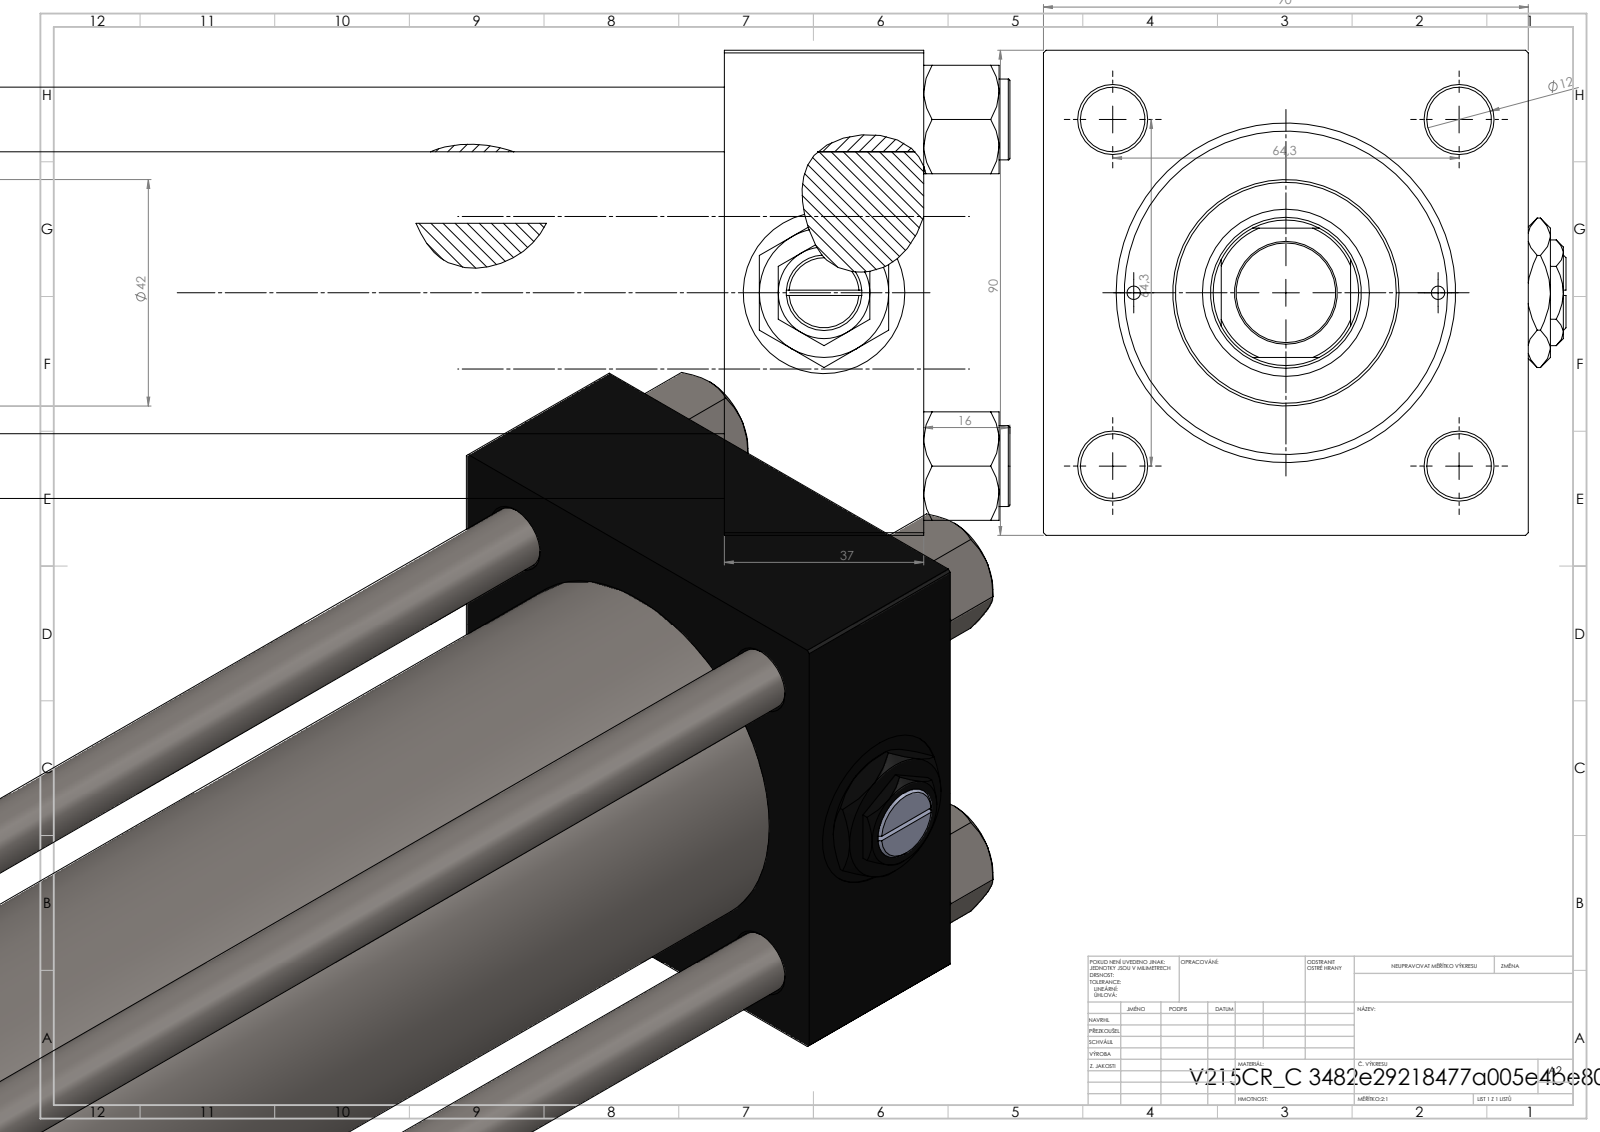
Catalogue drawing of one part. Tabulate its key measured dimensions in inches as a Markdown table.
| quantity | value |
| --- | --- |
| part name | V215CR_VCP_C; V215_VC_A; V215CR_C_Body; V215CR_C_TYCINKA (+2 more) |
| STEP written by | SolidWorks 2019 (CONFIG_CONTROL_DESIGN) |
| units | inches |
| bodies | 13 solids, 1256 faces (576 planar, 102 cylindrical, 578 other) |
| overall size | 17.047 × 3.819 × 3.543 |
| volume | 81.1 in³ |
| surface area | 518.1 in² |
| round holes (diameter × count) | 0.472 × 4, 0.098 × 2, 0.276 × 2, 0.825 × 2, 1.181 × 2, 0.728 × 1, 1.102 × 1, 1.22 × 1, 1.969 × 1, 2.362 × 1, 2.48 × 1 |
| round bosses / shafts (diameter × count) | 0.591 × 4, 2.717 × 1, 1.654 × 1 |
| partial cylindrical surfaces (radius × count) | 0.531 × 1 |
| main face-to-face distances | 3.543, 1.457, 13.701, 15.157, 2.323, 12.835, 11.378, 14.028, 12.571, 1.193 |
| hole center spacings | 1.275, 1.79, 2.531, 2.694, 1.112, 3.58, 2.224, 12.894 |
